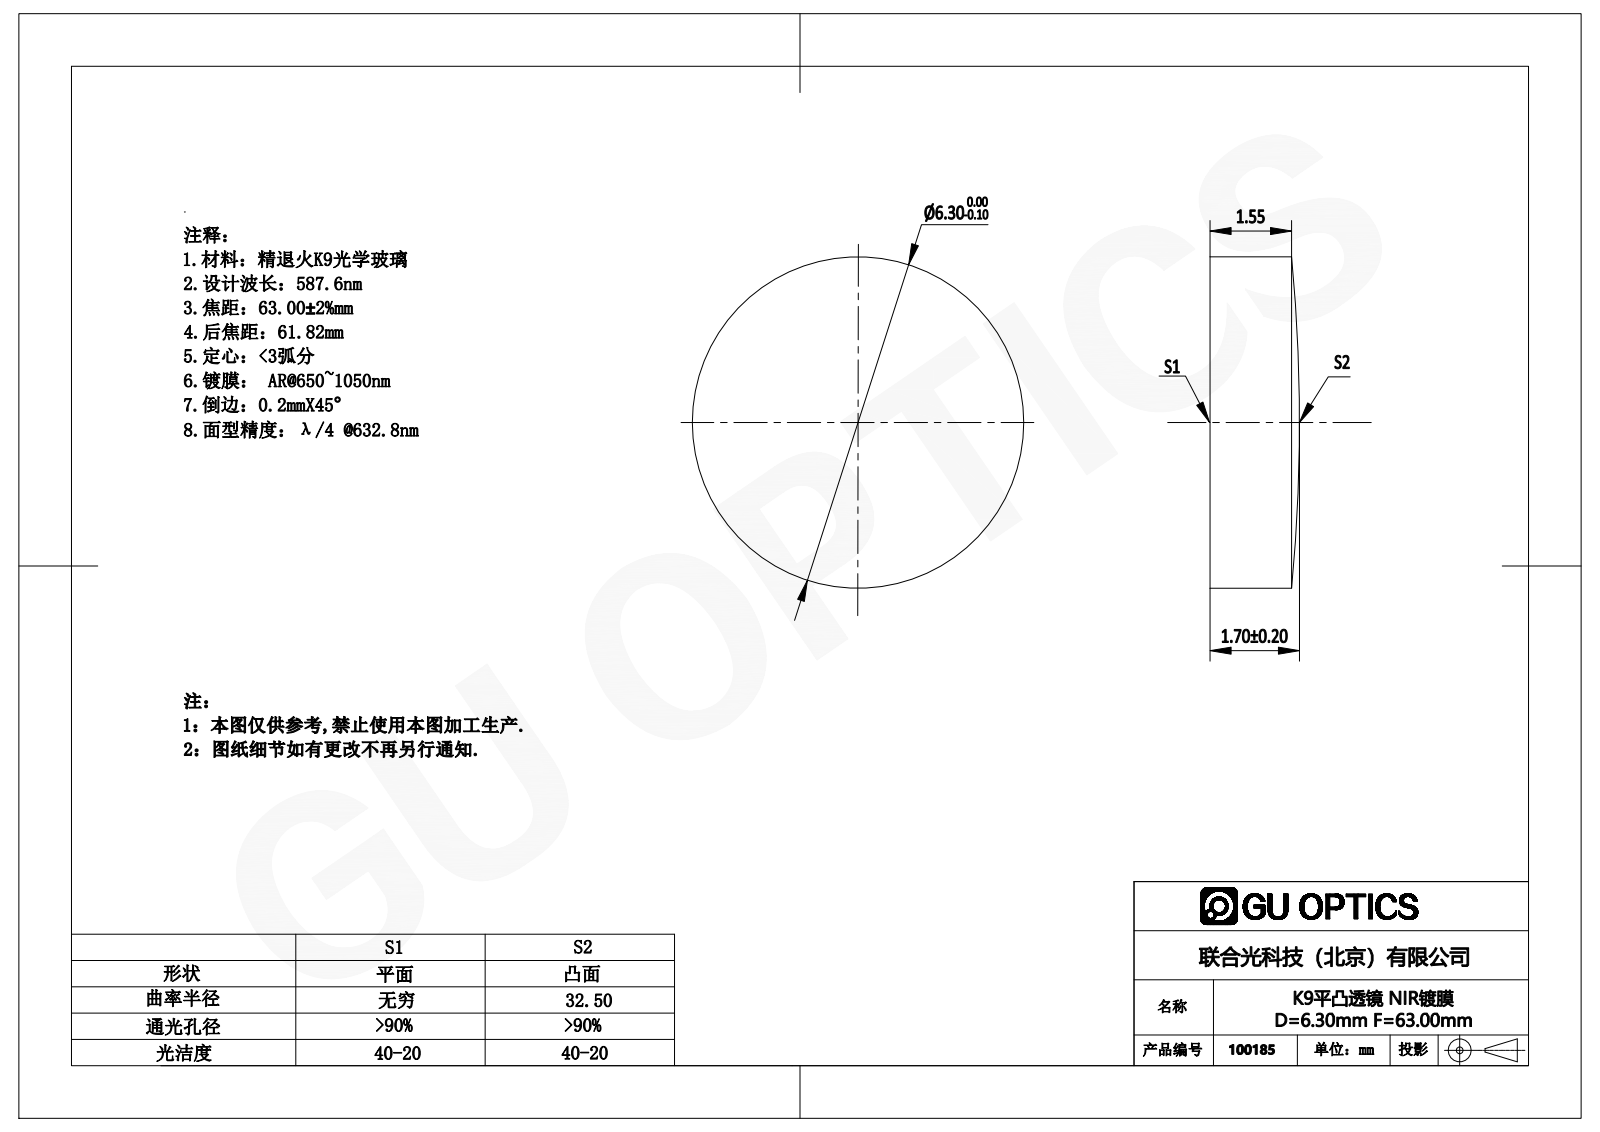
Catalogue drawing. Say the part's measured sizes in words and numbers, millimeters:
The part is named "100185". Its 3-D file was written by "SolidWorks 2016 (AUTOMOTIVE_DESIGN)". It is 1 solid with 5 faces: 1 planar, 2 cylindrical and 2 other. Overall it measures 6.3 by 6.3 by 1.7 millimeters. Its volume is 51 cubic millimeters and its surface area 93 square millimeters. Round bosses or shafts: 1 of diameter 6.3.
